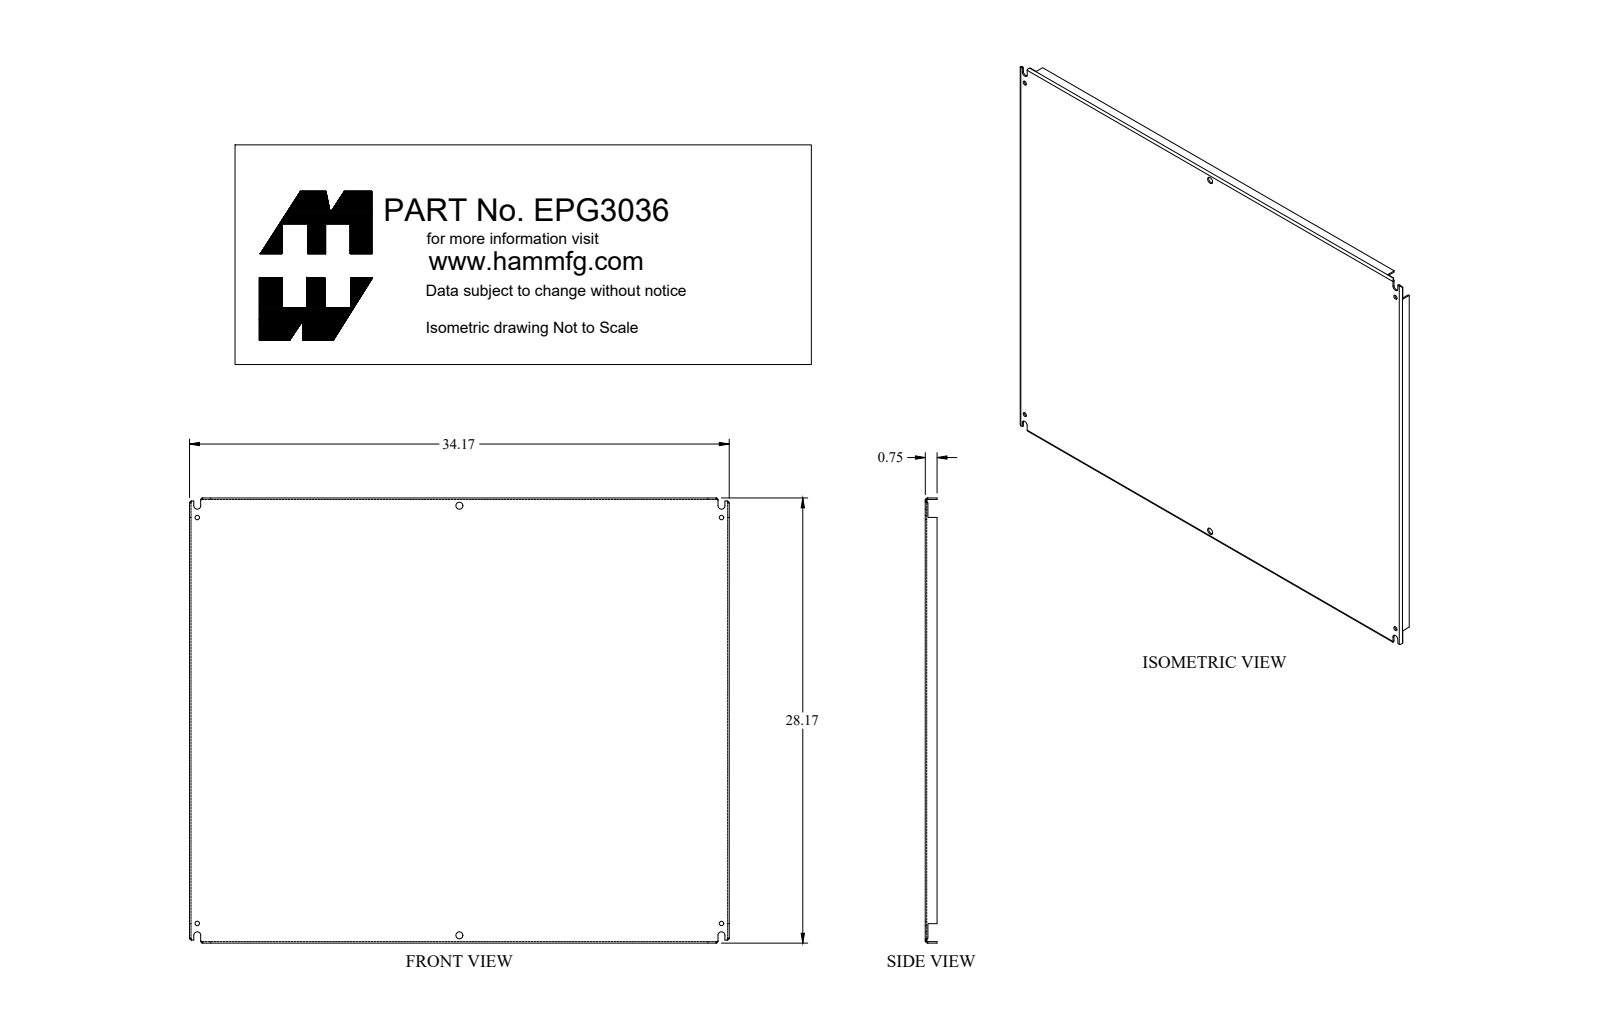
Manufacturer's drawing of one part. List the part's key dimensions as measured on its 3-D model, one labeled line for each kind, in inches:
Part name (STEP PRODUCT): EPG3036
STEP written by: SolidWorks 2018 (AUTOMOTIVE_DESIGN)
Units: inches
Bodies: 1 solid, 132 faces (74 planar, 42 cylindrical, 16 other)
Overall size (bounding box): 34.17 × 28.17 × 0.75
Volume: 97.94 in³ · Surface area: 2 075 in²
Round holes (diameter × count): ⌀0.281 ×4, ⌀0.437 ×2
Partial cylindrical surfaces — rounded edges, fillets, slot ends (radius × count): R0.048 ×4, R0.063 ×4, R0.143 ×4, R0.219 ×4
Main face-to-face distances: 0.095, 28.075, 34.075, 27.98, 28.17, 33.98, 34.17, 0.75, 0.655, 0.171
Hole centre spacings: 16.611, 31.215, 25.688, 33.188, 41.969, 27.188
